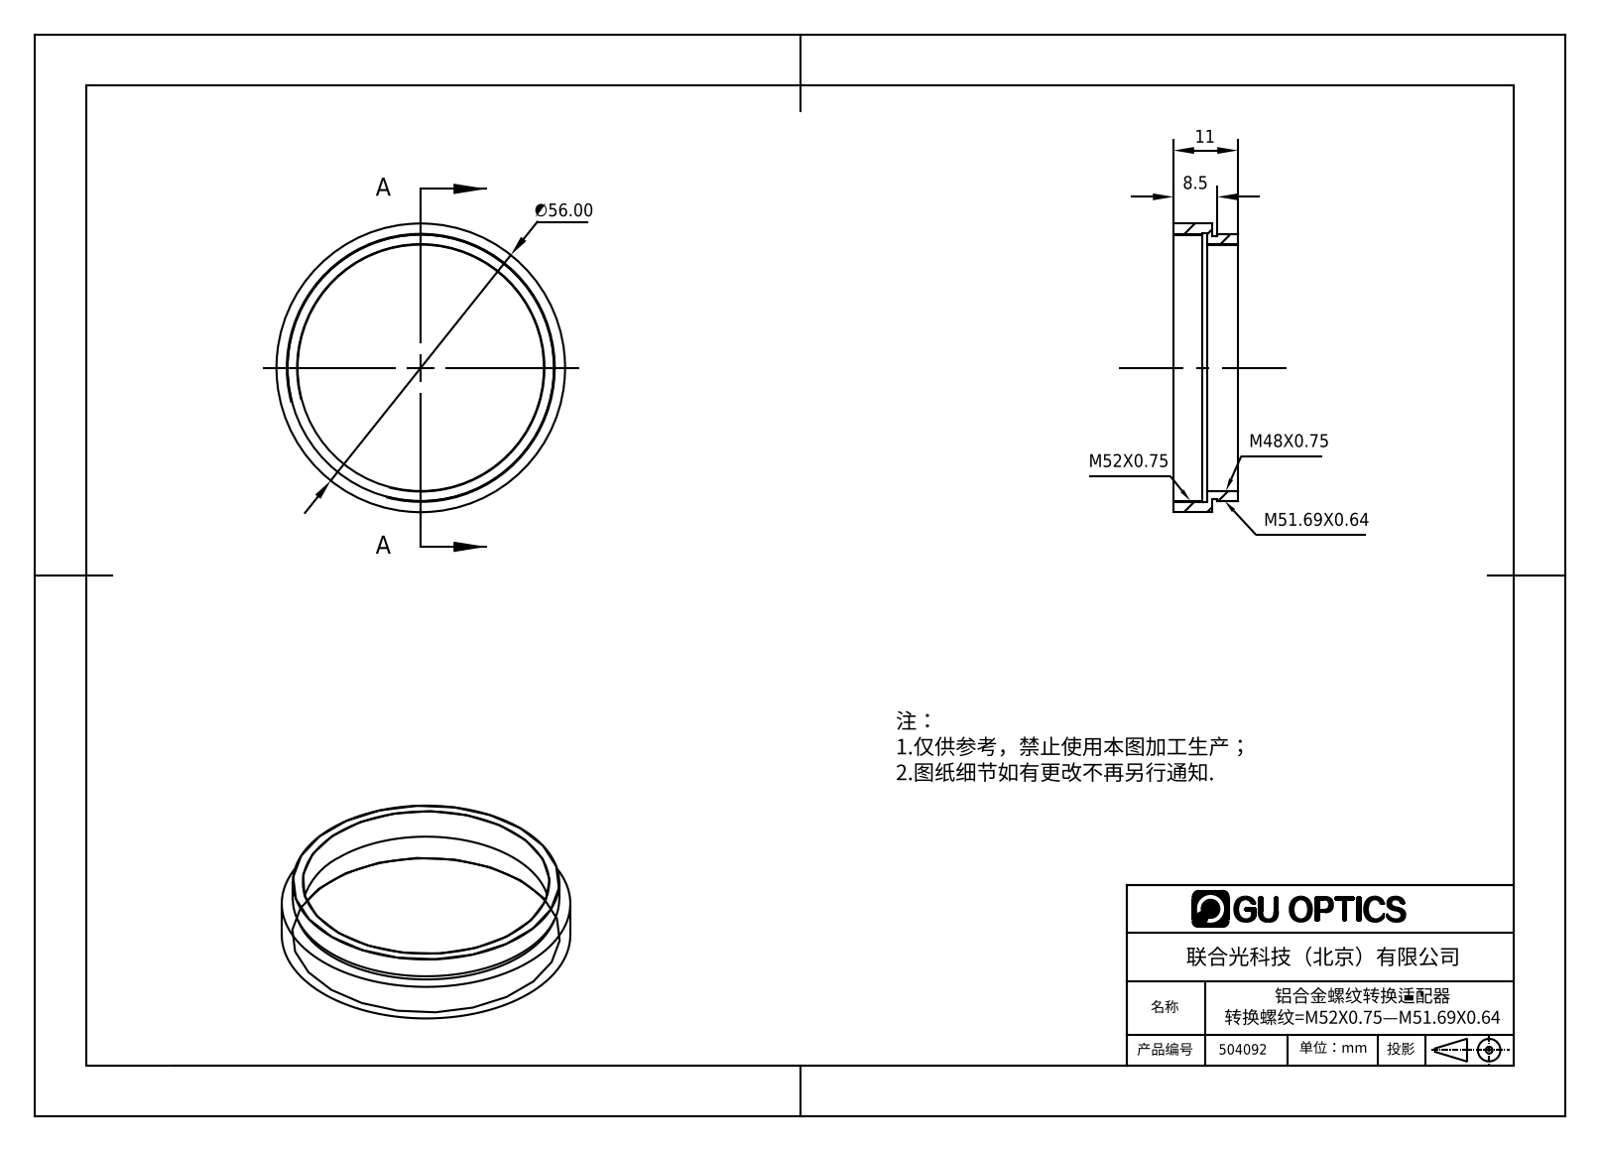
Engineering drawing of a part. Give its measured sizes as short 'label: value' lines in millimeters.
name: 504092
written by: SolidWorks 2016 (AUTOMOTIVE_DESIGN)
unit: mm
bodies: 1 solid, 18 faces (6 planar, 12 cylindrical, 0 other)
size: 56 × 56 × 11
volume: 4 343 mm³; area: 5 153 mm²
holes: 1× ⌀47.8, 1× ⌀51.6, 1× ⌀52.2
bosses: 1× ⌀56, 1× ⌀51.7, 1× ⌀51
face distances: 5.5, 7.5, 2, 11, 3.5, 1, 3, 8.5, 2.5, 4.5
